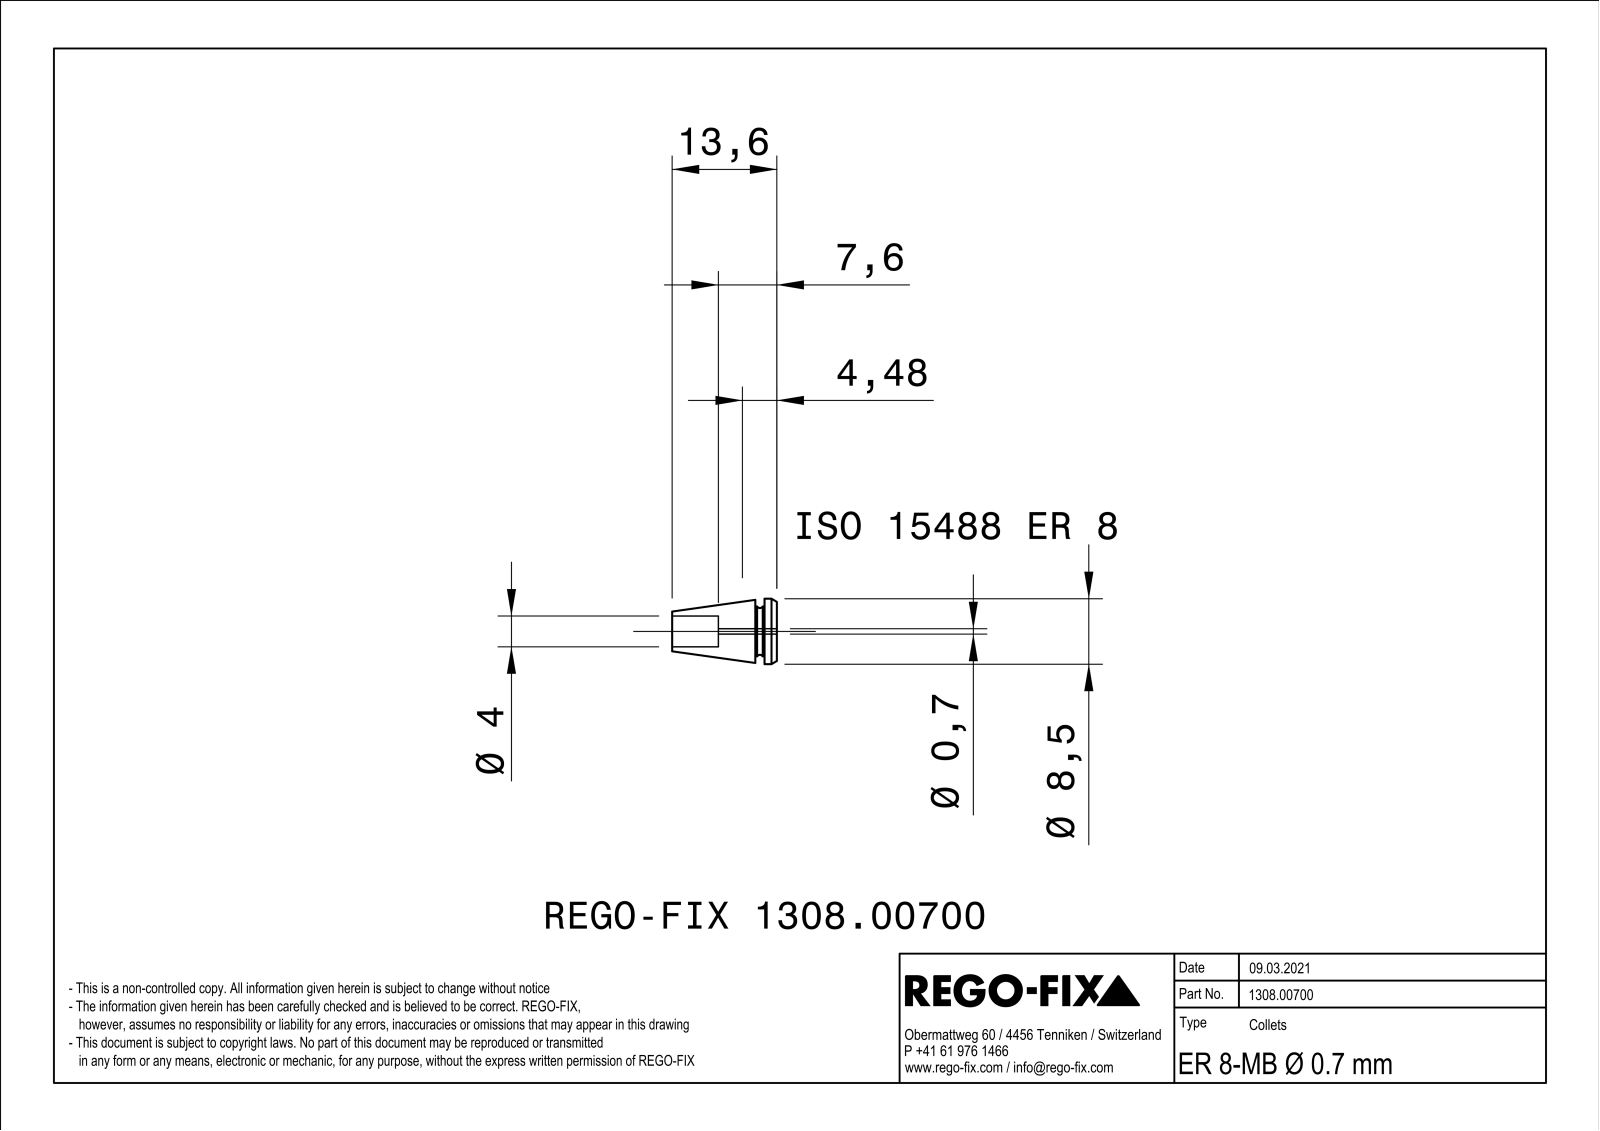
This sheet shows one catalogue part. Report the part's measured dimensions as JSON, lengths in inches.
{"part_name": "NOCUT", "step_written_by": "SIEMENS PLM Software Solid Edge ST10 (AUTOMOTIVE_DESIGN)", "units": "inches", "bodies": {"solids": 1, "faces": 83, "planar": 27, "cylindrical": 25, "other": 31}, "overall_size": [0.535, 0.335, 0.334], "volume_in3": 0.022, "surface_area_in2": 1.12, "round_holes": [[0.047, 3], [0.157, 1]], "round_bosses_or_shafts": [[0.335, 1], [0.256, 1]], "partial_cylinders_radius": [[0.984, 3], [0.014, 1]], "face_to_face_distances": [0.024, 0.063, 0.016, 0.11, 0.047, 0.236, 0.299, 0.189, 0.441, 0.378], "hole_center_spacings": [0.053, 0.092]}
